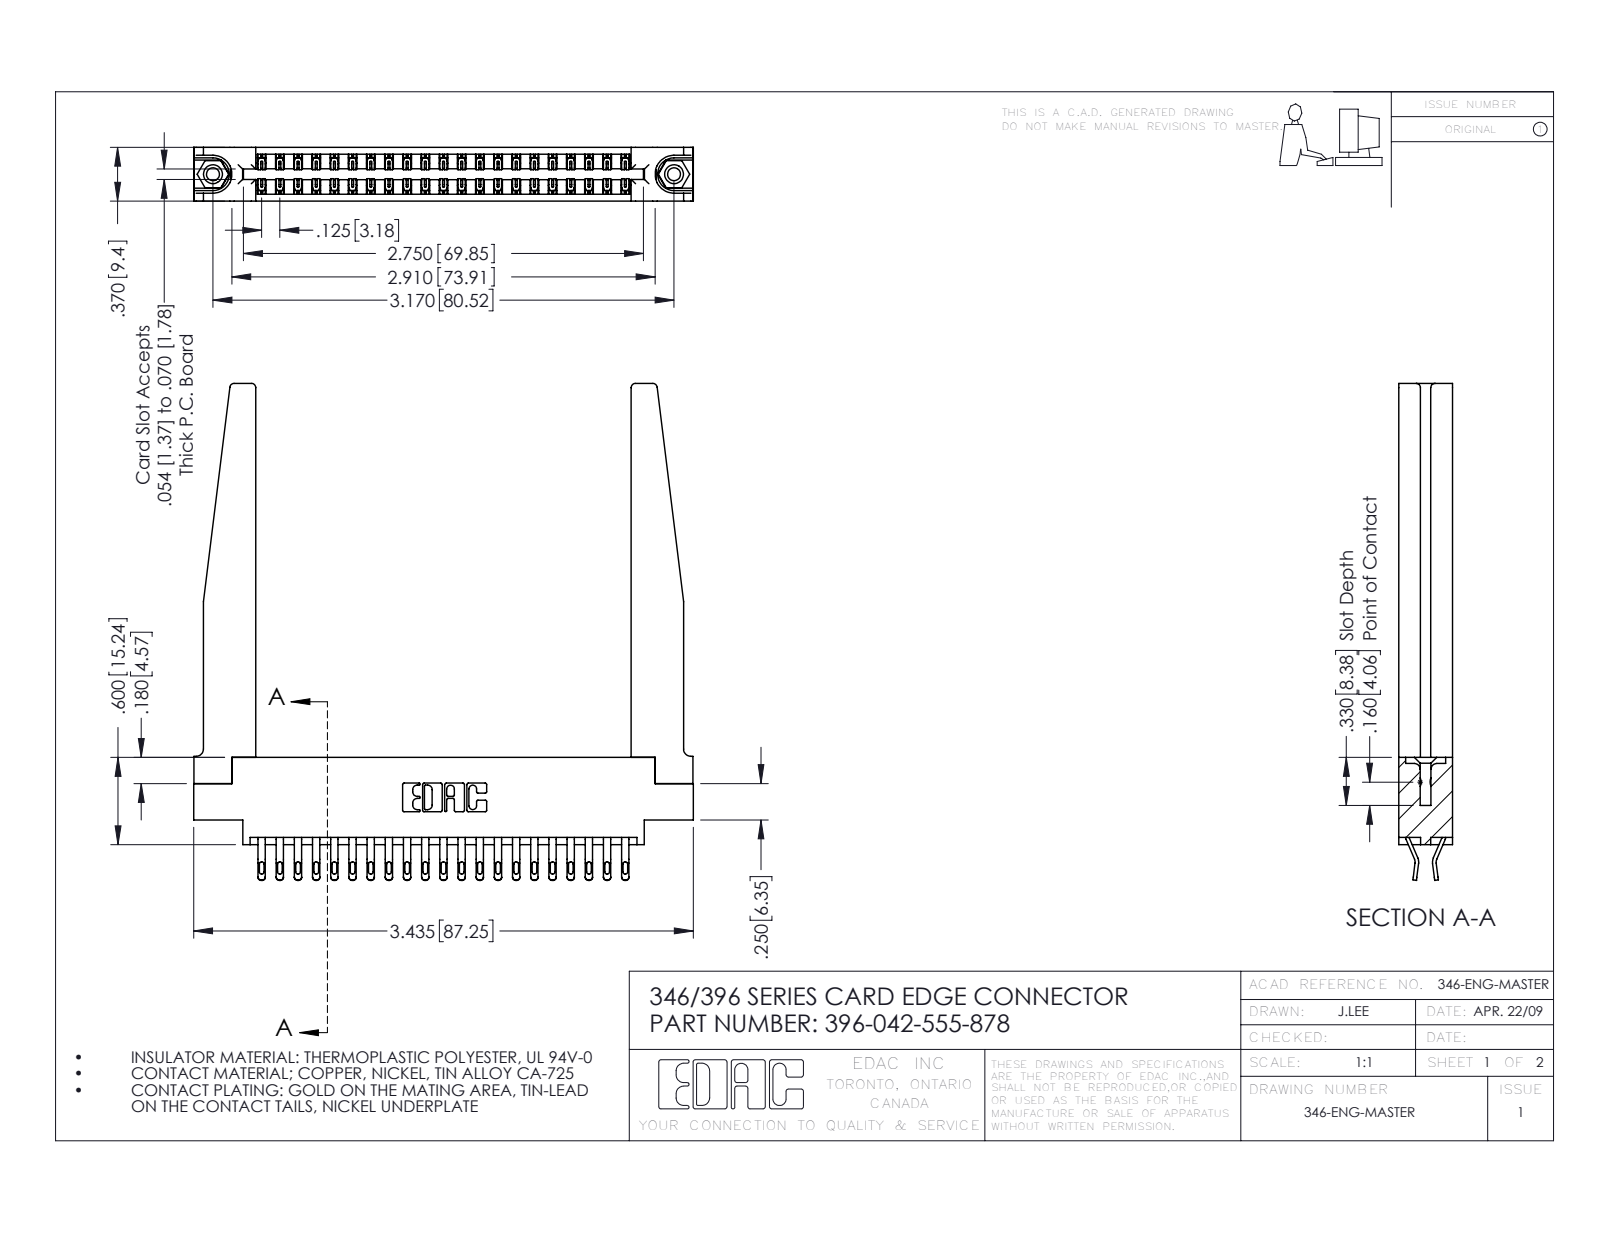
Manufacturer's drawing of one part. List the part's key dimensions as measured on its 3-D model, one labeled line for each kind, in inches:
Part name (STEP PRODUCT): 345-292-001_555 Tail; 346 Part_0.170 Offset - 0.156 Dia-TH; 345-250-001_345-250-001-102; 396-042-555-878 (+1 more)
STEP written by: SolidWorks 2016 (CONFIG_CONTROL_DESIGN)
Units: inches
Bodies: 47 solids, 2796 faces (1608 planar, 1136 cylindrical, 52 other)
Overall size (bounding box): 3.435 × 3.415 × 0.37
Volume: 0.929 in³ · Surface area: 28.28 in²
Round holes (diameter × count): ⌀0.089 ×2, ⌀0.125 ×2, ⌀0.156 ×2, ⌀0.064 ×1
Round bosses / shafts (diameter × count): ⌀0.155 ×2
Partial cylindrical surfaces — rounded edges, fillets, slot ends (radius × count): R0.016 ×84, R0.02 ×84, R0.006 ×63, R0.01 ×22, R0.03 ×8, R0.007 ×6, R0.031 ×6, R0.05 ×4
Main face-to-face distances: 0.37, 0.048, 0.322, 0.072, 0.148, 0.15, 0.25, 0.025, 0.298, 0.275
Hole centre spacings: 0.246, 2.963, 3.17
